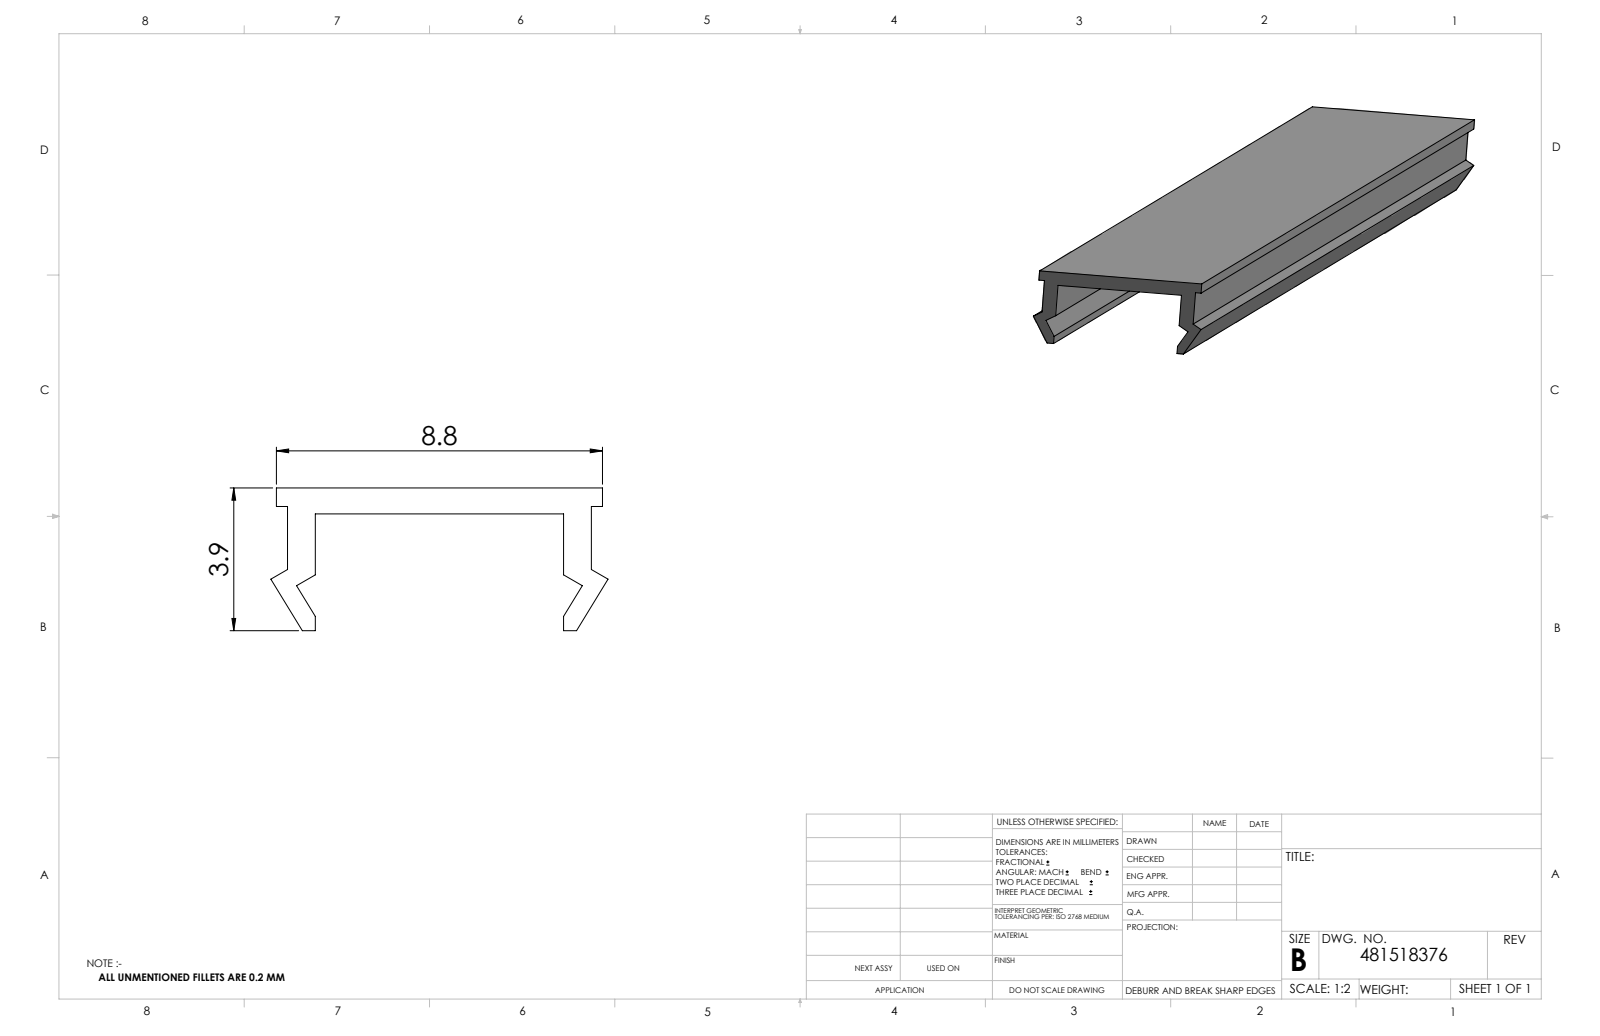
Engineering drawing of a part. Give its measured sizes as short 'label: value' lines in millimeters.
name: 481518376_c_1
written by: SolidWorks 2014 (CONFIG_CONTROL_DESIGN)
unit: mm
bodies: 1 solid, 24 faces (24 planar, 0 cylindrical, 0 other)
size: 200 × 9.1 × 3.85
volume: 2 077 mm³; area: 6 554 mm²
face distances: 0.7, 0.5, 0.75, 7.45, 6.7, 8.2, 1.05, 7.75, 8.5, 3.15
